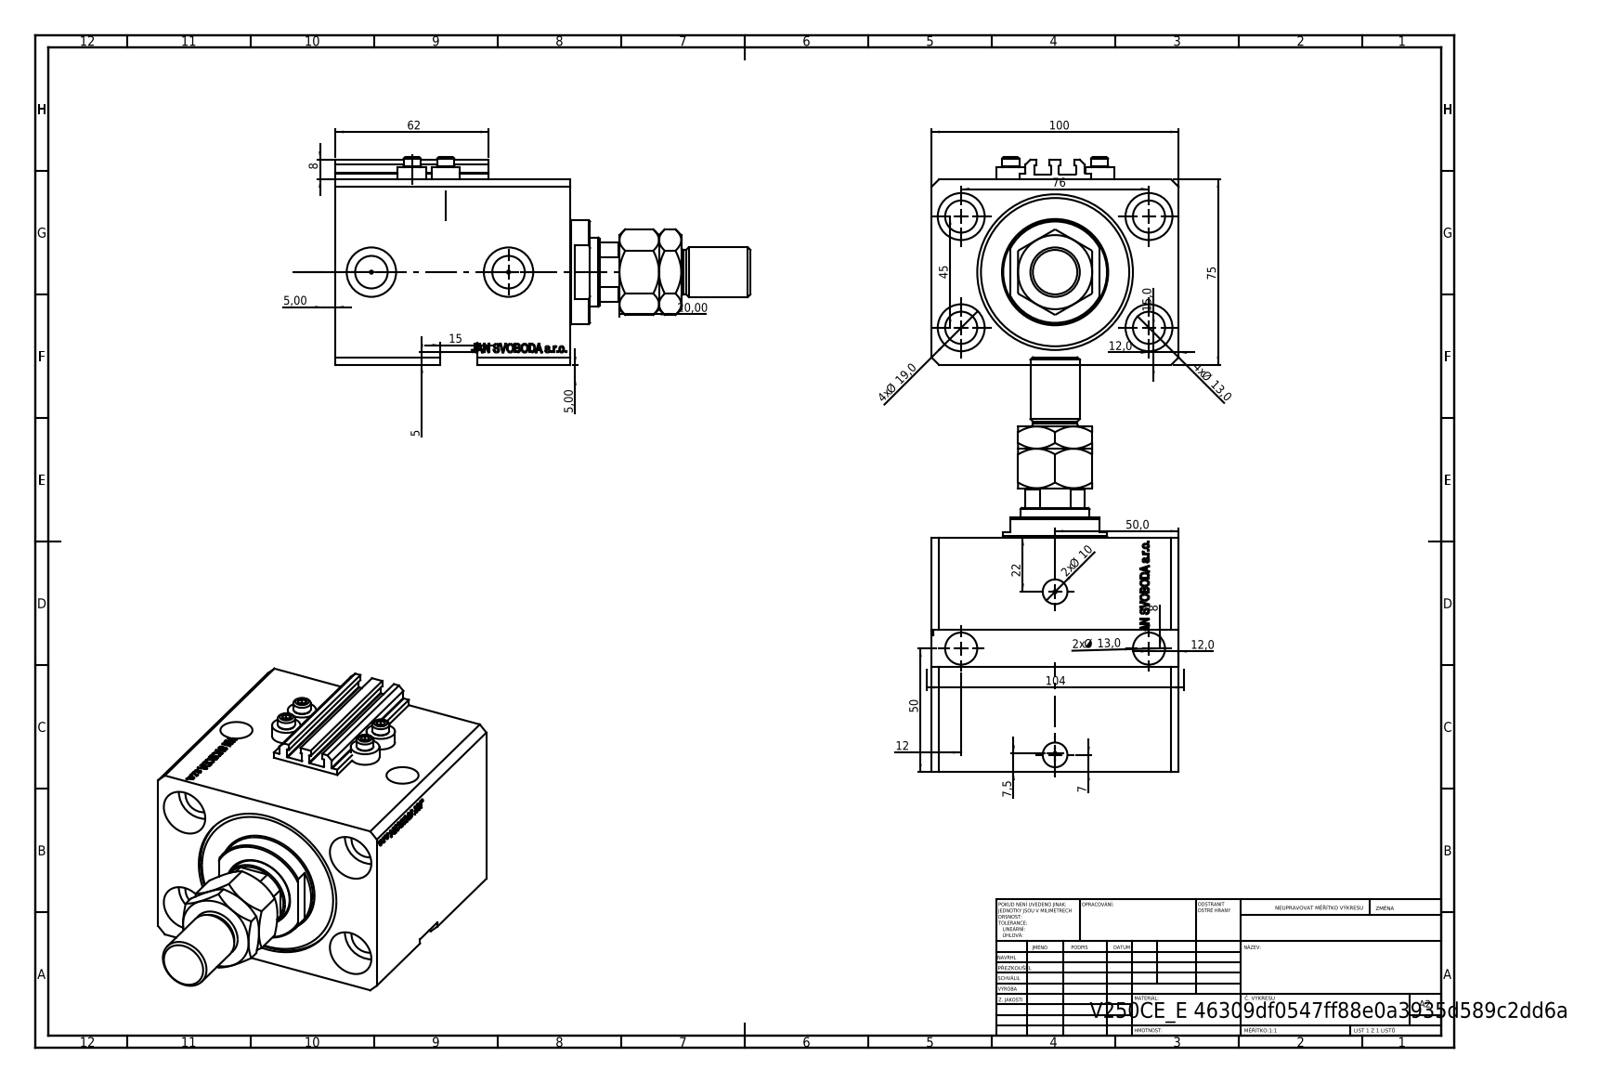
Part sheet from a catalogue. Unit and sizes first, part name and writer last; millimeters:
Units: millimetres
Overall size (bounding box): 167.9 × 100 × 84
Round holes (diameter × count): ⌀13 ×6, ⌀1.25 ×4, ⌀4 ×4, ⌀19 ×4, ⌀10 ×2, ⌀13.16 ×2, ⌀20 ×2, ⌀18.5 ×1, ⌀28 ×1, ⌀50 ×1, ⌀63 ×1
Round bosses / shafts (diameter × count): ⌀11.6 ×4, ⌀7 ×4, ⌀42 ×1, ⌀20 ×1, ⌀18 ×1
Partial cylindrical surfaces — rounded edges, fillets, slot ends (radius × count): R0.2 ×10, R13.5 ×1
Main face-to-face distances: 75, 100, 95, 11.9, 83.1, 68.4, 56.5, 26.6, 3, 5
Hole centre spacings: 44.16, 76, 13.6, 20.72, 27.59, 29.58, 30, 33.62
Volume: 638 844 mm³ · Surface area: 129 391 mm²
Bodies: 9 solids, 1137 faces (550 planar, 130 cylindrical, 457 other)
Part name (STEP PRODUCT): V250CE_VC_E; MTA; V250CE_E_Body; ALLEN BOLT V250CE (+1 more)
STEP written by: SolidWorks 2019 (CONFIG_CONTROL_DESIGN)
